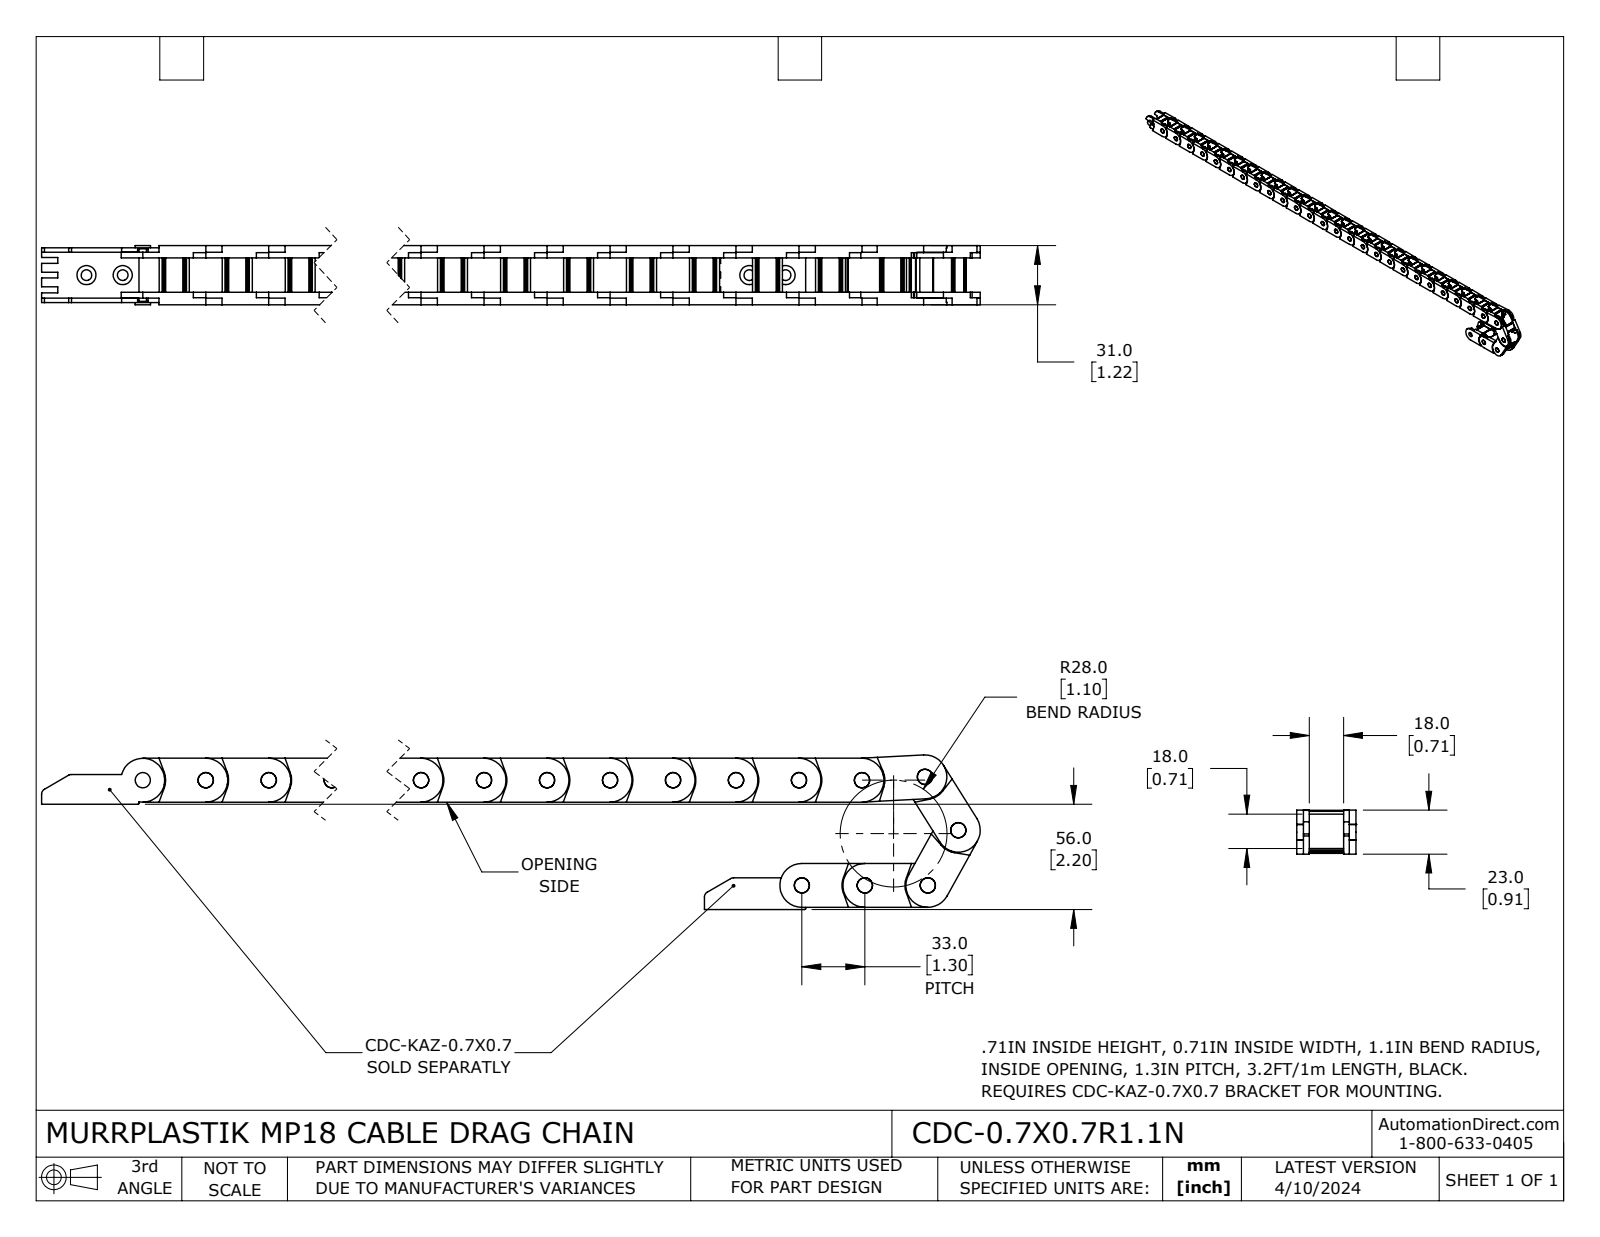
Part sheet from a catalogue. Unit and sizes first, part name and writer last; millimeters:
Units: millimetres
Overall size (bounding box): 898.29 × 79.84 × 31
Round holes (diameter × count): ⌀8 ×30
Round bosses / shafts (diameter × count): ⌀8 ×1
Partial cylindrical surfaces — rounded edges, fillets, slot ends (radius × count): R0.5 ×120, R1.5 ×120, R0.2 ×60, R0.3 ×60, R11.5 ×31, R11.95 ×31, R5 ×30, R5.45 ×30
Main face-to-face distances: 6.5, 24.5, 31, 18, 3.5, 27.5, 3, 21, 3.7, 27.3
Hole centre spacings: 33, 66, 99, 132, 165, 198, 231, 264
Volume: 298 198 mm³ · Surface area: 212 463 mm²
Bodies: 30 solids, 2790 faces (1530 planar, 1260 cylindrical, 0 other)
Part name (STEP PRODUCT): CDC-0.7X0.7R1.1N
STEP written by: SolidWorks 2023 (CONFIG_CONTROL_DESIGN)
